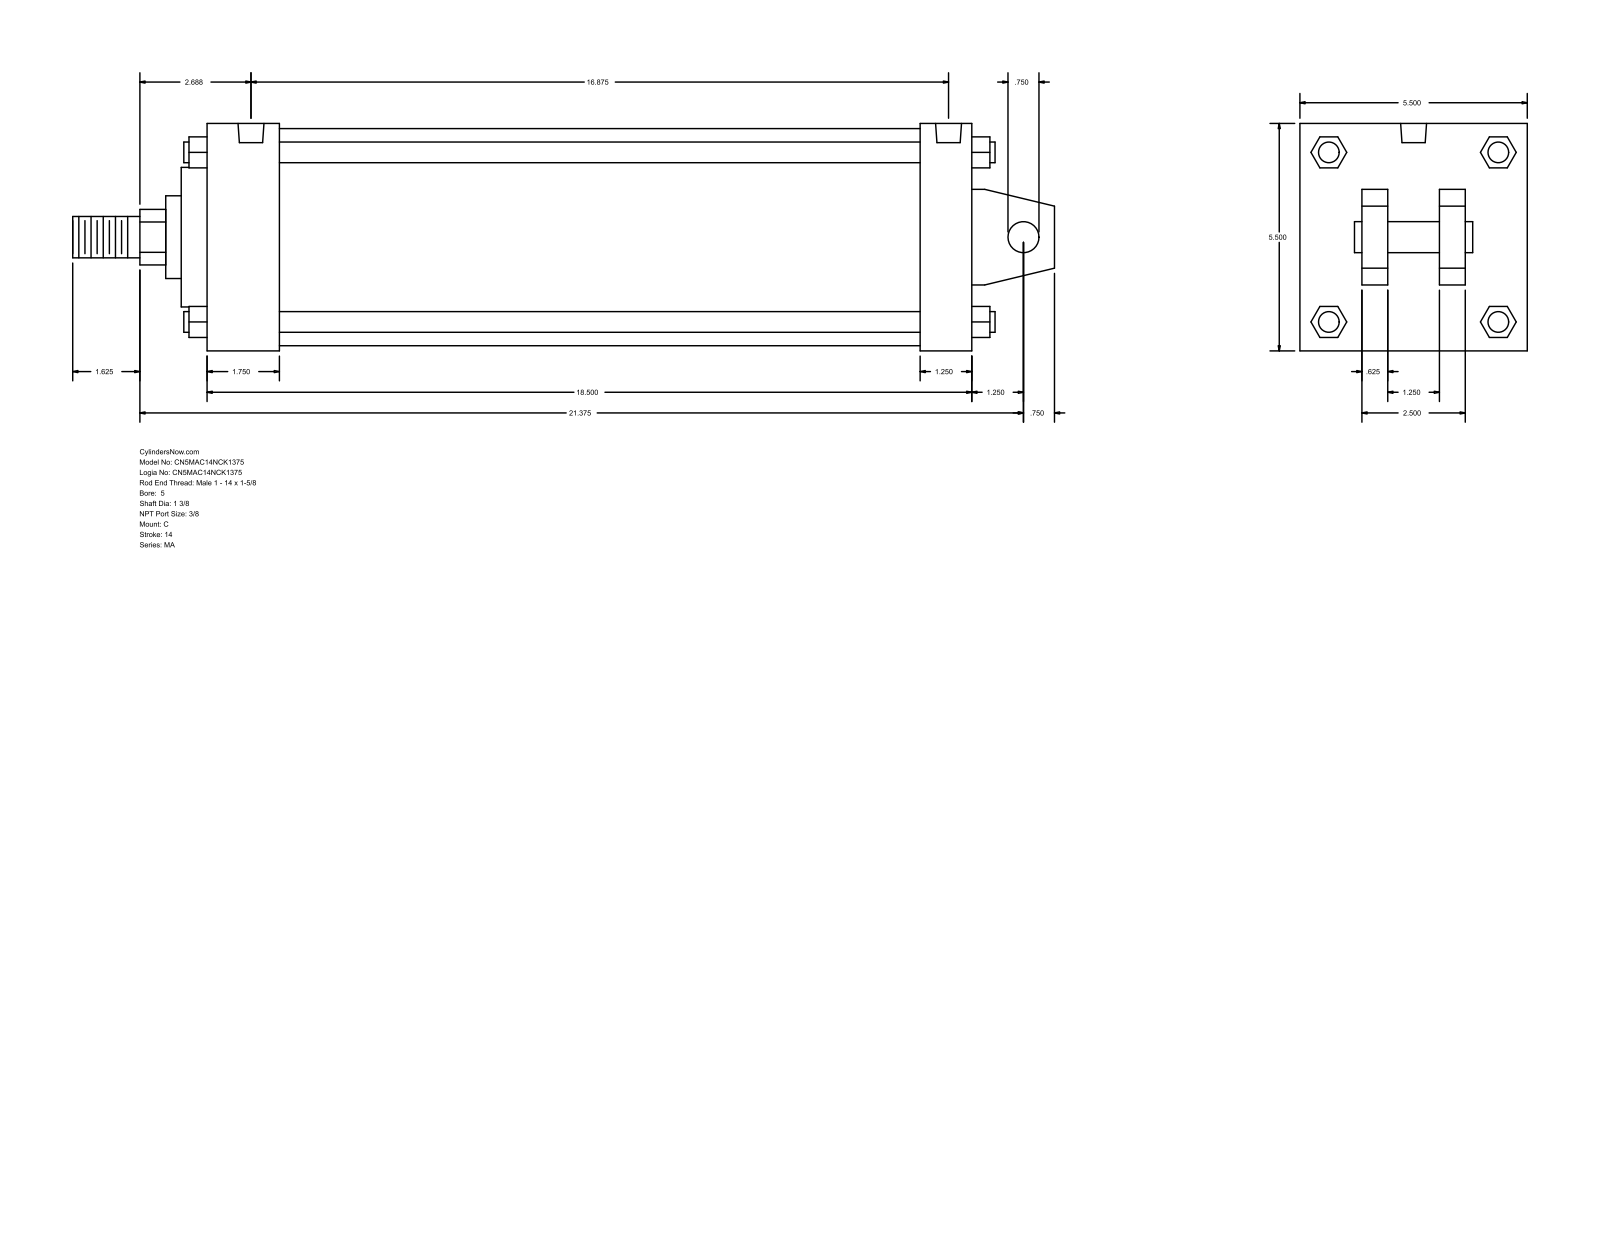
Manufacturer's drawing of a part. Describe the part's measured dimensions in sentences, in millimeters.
The part is named "MA_C__0500_1.375". Its 3-D file was written by "GSSL Pune (CONFIG_CONTROL_DESIGN)". It is 0 solids with 141 faces: 109 planar, 32 cylindrical and 0 other. Overall it measures 603.25 by 139.7 by 139.7 millimeters. Round holes: 4 of diameter 11.11, 2 of diameter 15.93. Round bosses or shafts: 4 of diameter 12.7, 1 of diameter 133.35, 1 of diameter 85.72, 1 of diameter 50.8, 1 of diameter 34.92, 1 of diameter 25.4, 1 of diameter 19.05. Partial cylindrical surfaces (rounded edges, fillets, slot ends): 1 of radius 17.06. The main face-to-face distances are 139.7, 469.91, 15.87, 438.16, 31.75, 44.45, 393.71, 425.46, 53.97, 38.1. The hole center spacings are 4.77, 419.09, 423.86, 428.63.
